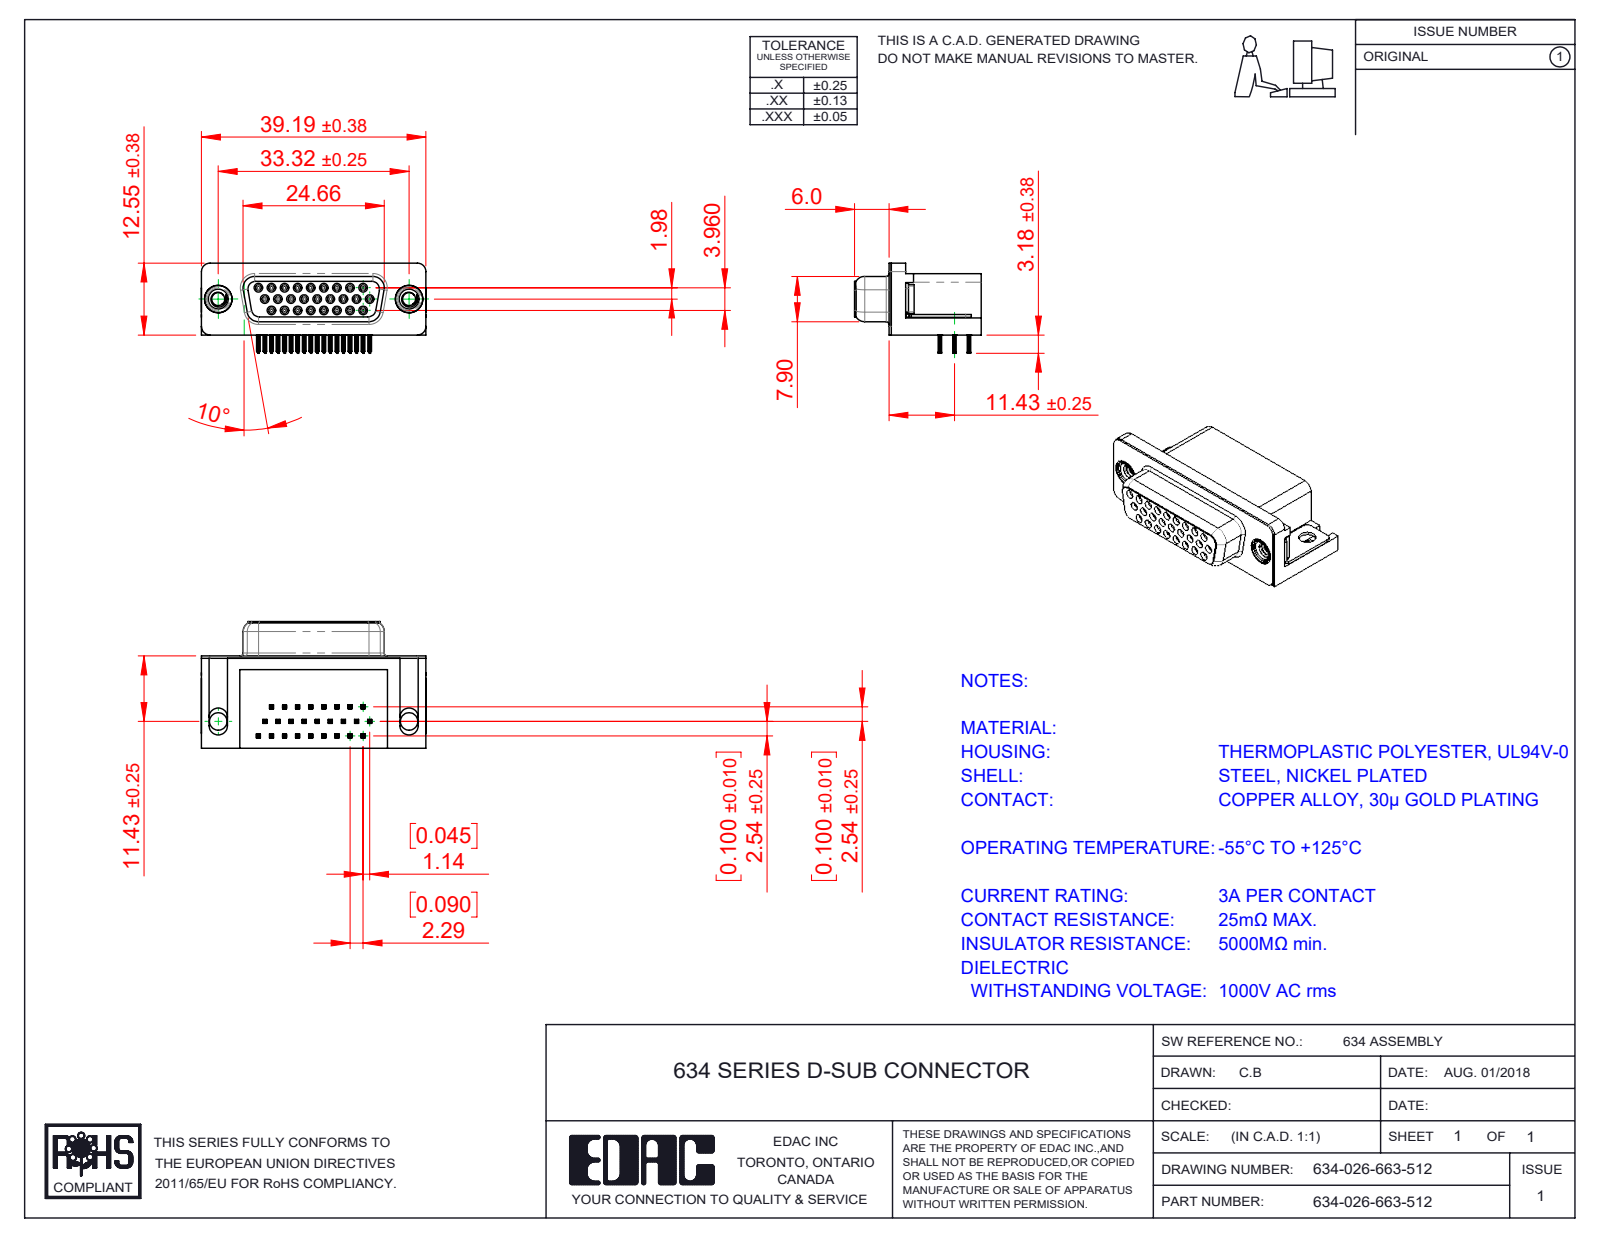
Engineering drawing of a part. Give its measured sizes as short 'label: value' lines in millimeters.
name: 4-40 Threaded Rivet; Thru Hole Board Mount; 634 Housing_26 Socket; 634-026-663-512 (+4 more)
written by: SolidWorks 2016 (CONFIG_CONTROL_DESIGN)
unit: mm
bodies: 32 solids, 3979 faces (1769 planar, 938 cylindrical, 1272 other)
size: 39.22 × 22.1 × 15.73
volume: 6 365 mm³; area: 9 068 mm²
holes: 26× ⌀0.8, 26× ⌀0.9, 2× ⌀2.26, 2× ⌀3.05, 2× ⌀4, 2× ⌀4.8, 2× ⌀5
bosses: 26× ⌀1.2, 2× ⌀4.9, 2× ⌀4.75, 2× ⌀3.9
rounds: 208× R0.1, 104× R0.15, 52× R0.35, 26× R0.34, 19× R1, 8× R0.25, 8× R0.28, 8× R1.35
face distances: 0.4, 10.34, 0.35, 15.7, 16.1, 6.65, 2.5, 0.85, 2.9, 10.69
hole spacings: 2.29, 4.57, 2.28, 3.96, 6.05, 2.3, 2.27, 4.58
